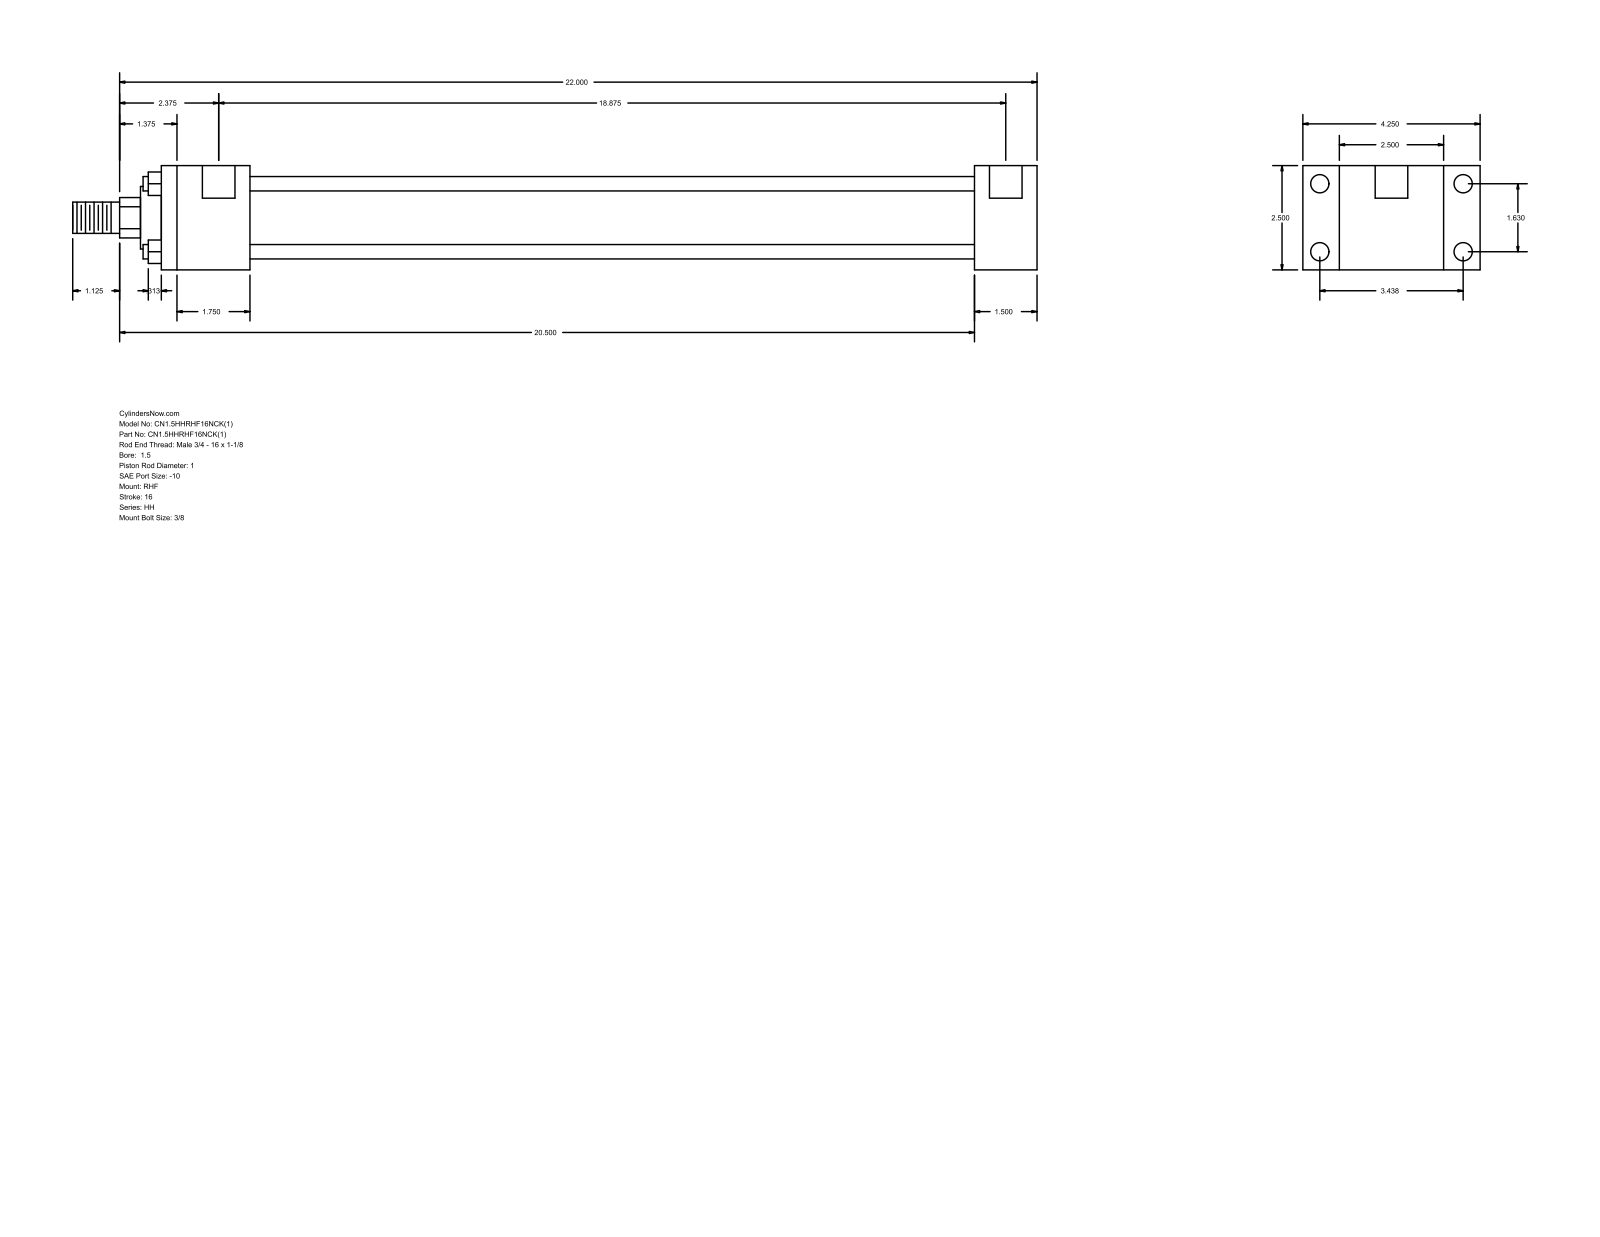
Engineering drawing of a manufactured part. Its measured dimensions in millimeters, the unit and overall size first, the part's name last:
Units: millimetres
Overall size (bounding box): 587.38 × 107.95 × 63.5
Round holes (diameter × count): ⌀5.56 ×4, ⌀11.13 ×4, ⌀19.84 ×2
Round bosses / shafts (diameter × count): ⌀8.76 ×4, ⌀44.45 ×1, ⌀38.1 ×1, ⌀25.4 ×1, ⌀19.05 ×1
Partial cylindrical surfaces — rounded edges, fillets, slot ends (radius × count): R12.29 ×1
Main face-to-face distances: 63.5, 22.23, 85.73, 38.1, 107.96, 441.32, 479.42, 53.98, 495.3, 533.4
Hole centre spacings: 1.59, 41.4, 87.32, 96.64, 481.01, 482.6, 479.42
Bodies: 0 solids, 88 faces (60 planar, 28 cylindrical, 0 other)
Part name (STEP PRODUCT): HH_RHF__0150_1
STEP written by: GSSL Pune (CONFIG_CONTROL_DESIGN)
